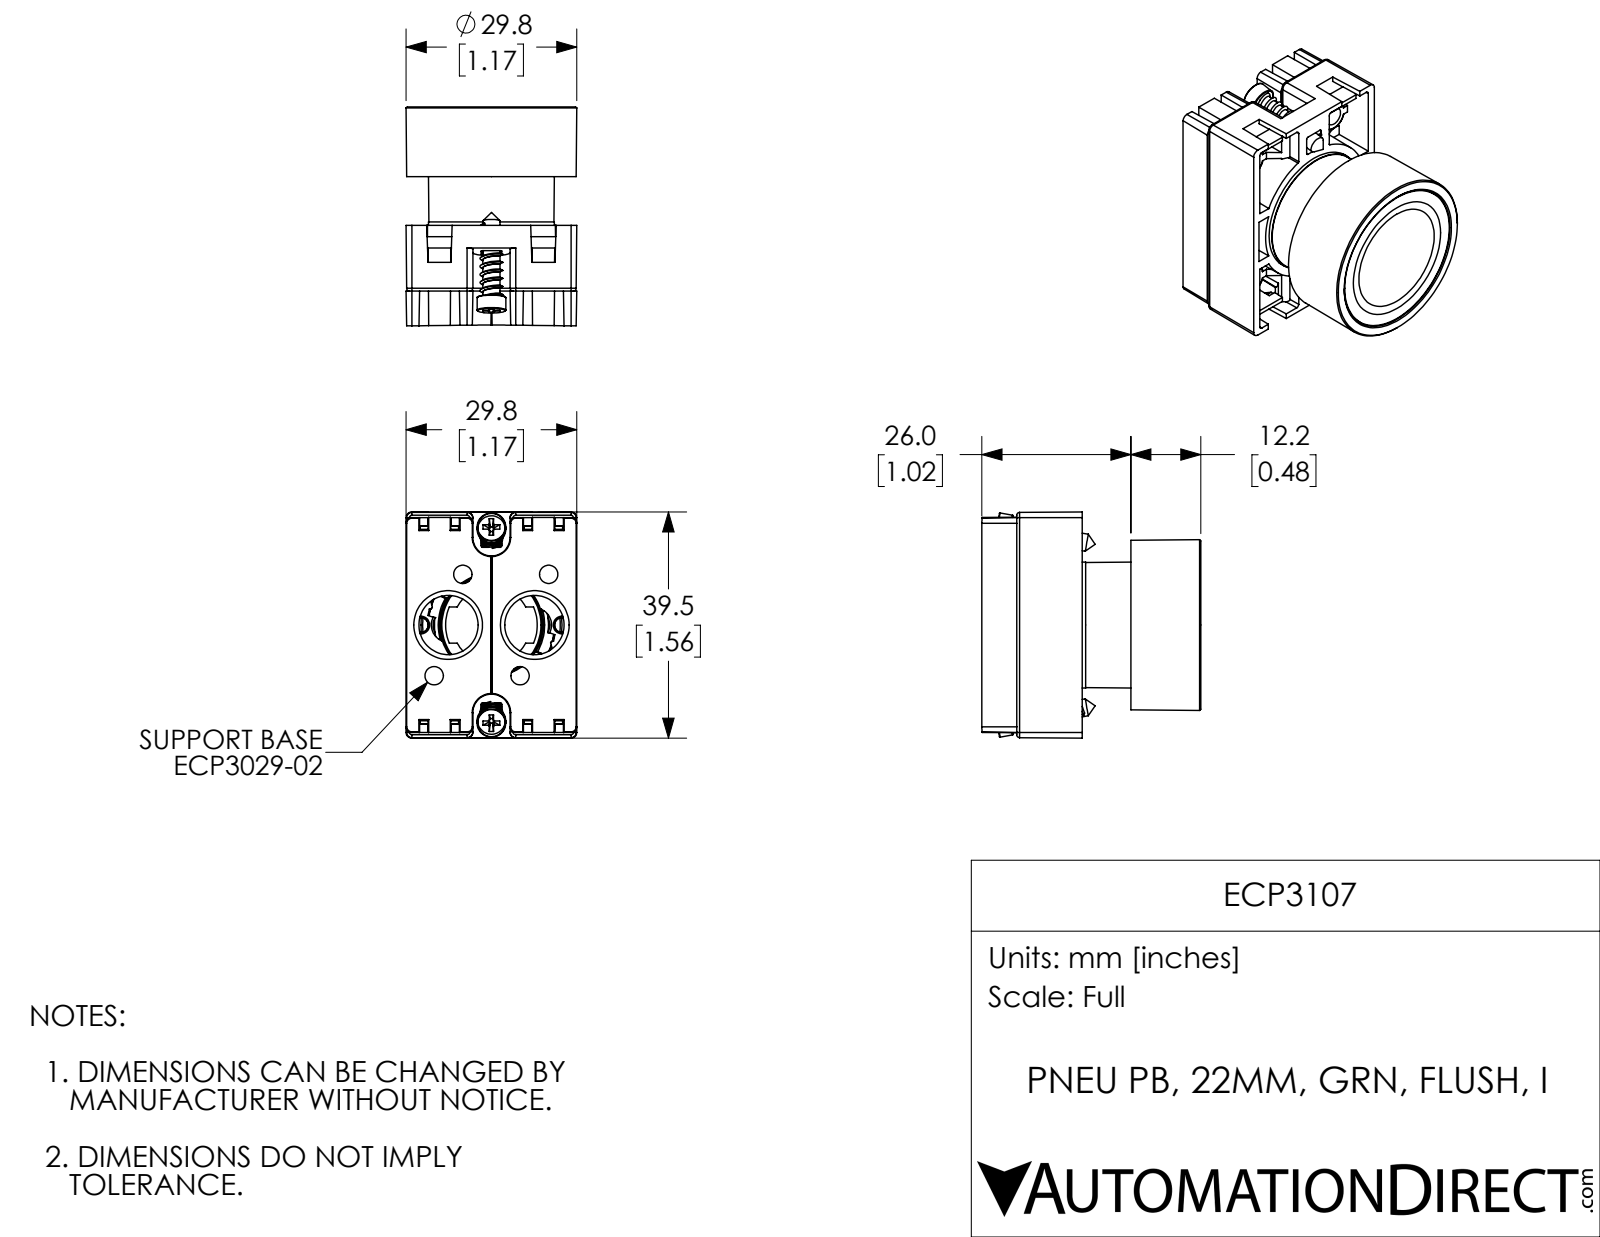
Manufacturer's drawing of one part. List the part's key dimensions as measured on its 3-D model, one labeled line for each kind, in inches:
Part name (STEP PRODUCT): ECP3107
STEP written by: SolidWorks 2017 (AUTOMOTIVE_DESIGN)
Units: inches
Bodies: 7 solids, 778 faces (363 planar, 131 cylindrical, 284 other)
Overall size (bounding box): 1.555 × 1.505 × 1.173
Volume: 0.893 in³ · Surface area: 29.03 in²
Round holes (diameter × count): ⌀0.081 ×4, ⌀0.407 ×2, ⌀0.697 ×1, ⌀0.732 ×1
Round bosses / shafts (diameter × count): ⌀0.197 ×2, ⌀0.118 ×2, ⌀1.016 ×1, ⌀0.866 ×1
Partial cylindrical surfaces — rounded edges, fillets, slot ends (radius × count): R0.02 ×18, R0.006 ×8, R0.012 ×8, R0.008 ×4, R0.039 ×4, R0.008 ×2, R0.118 ×2, R0.128 ×2
Main face-to-face distances: 1.195, 0.963, 0.177, 0.067, 0.715, 0.744, 0.451, 0.587, 0.519, 0.256
Hole centre spacings: 0.304, 0.541, 0.817, 0.295, 0.472, 0.972, 1.081, 0.591
